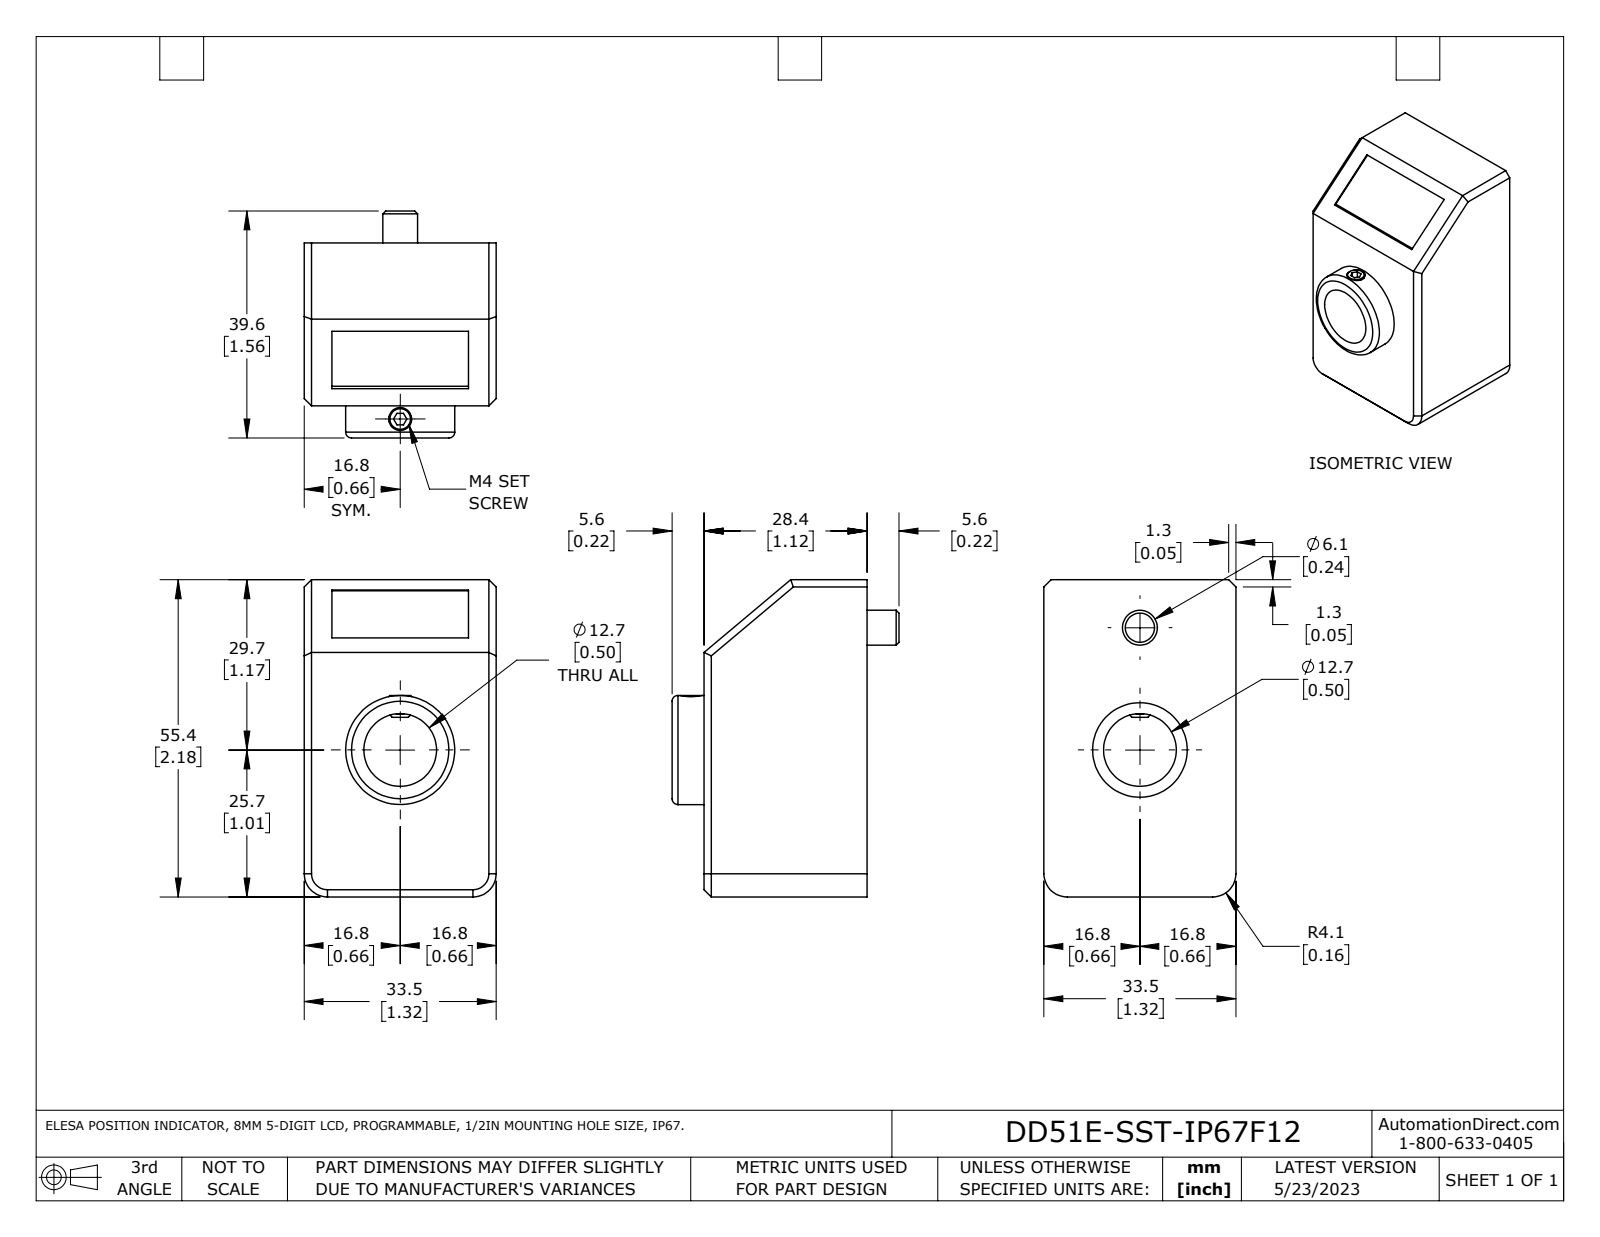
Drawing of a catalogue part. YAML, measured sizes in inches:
part_name: "DD51E-SST-IP67F12"
step_written_by: "SolidWorks 2021 (AUTOMOTIVE_DESIGN)"
units: inches
bodies: {solids: 1, faces: 55, planar: 37, cylindrical: 12, other: 6}
overall_size: [2.18, 1.56, 1.32]
volume: 2.769
surface_area: 16.13
round_holes:
  - {diameter: 0.157, count: 1}
  - {diameter: 0.5, count: 1}
  - {diameter: 0.65, count: 1}
round_bosses_or_shafts:
  - {diameter: 0.75, count: 1}
  - {diameter: 0.24, count: 1}
partial_cylinders:
  - {radius: 0.16, count: 2}
face_to_face_distances: [1.32, 1.12, 2.18, 0.014, 0.52, 1.78, 0.4, 0.6, 0.22, 1.34]
